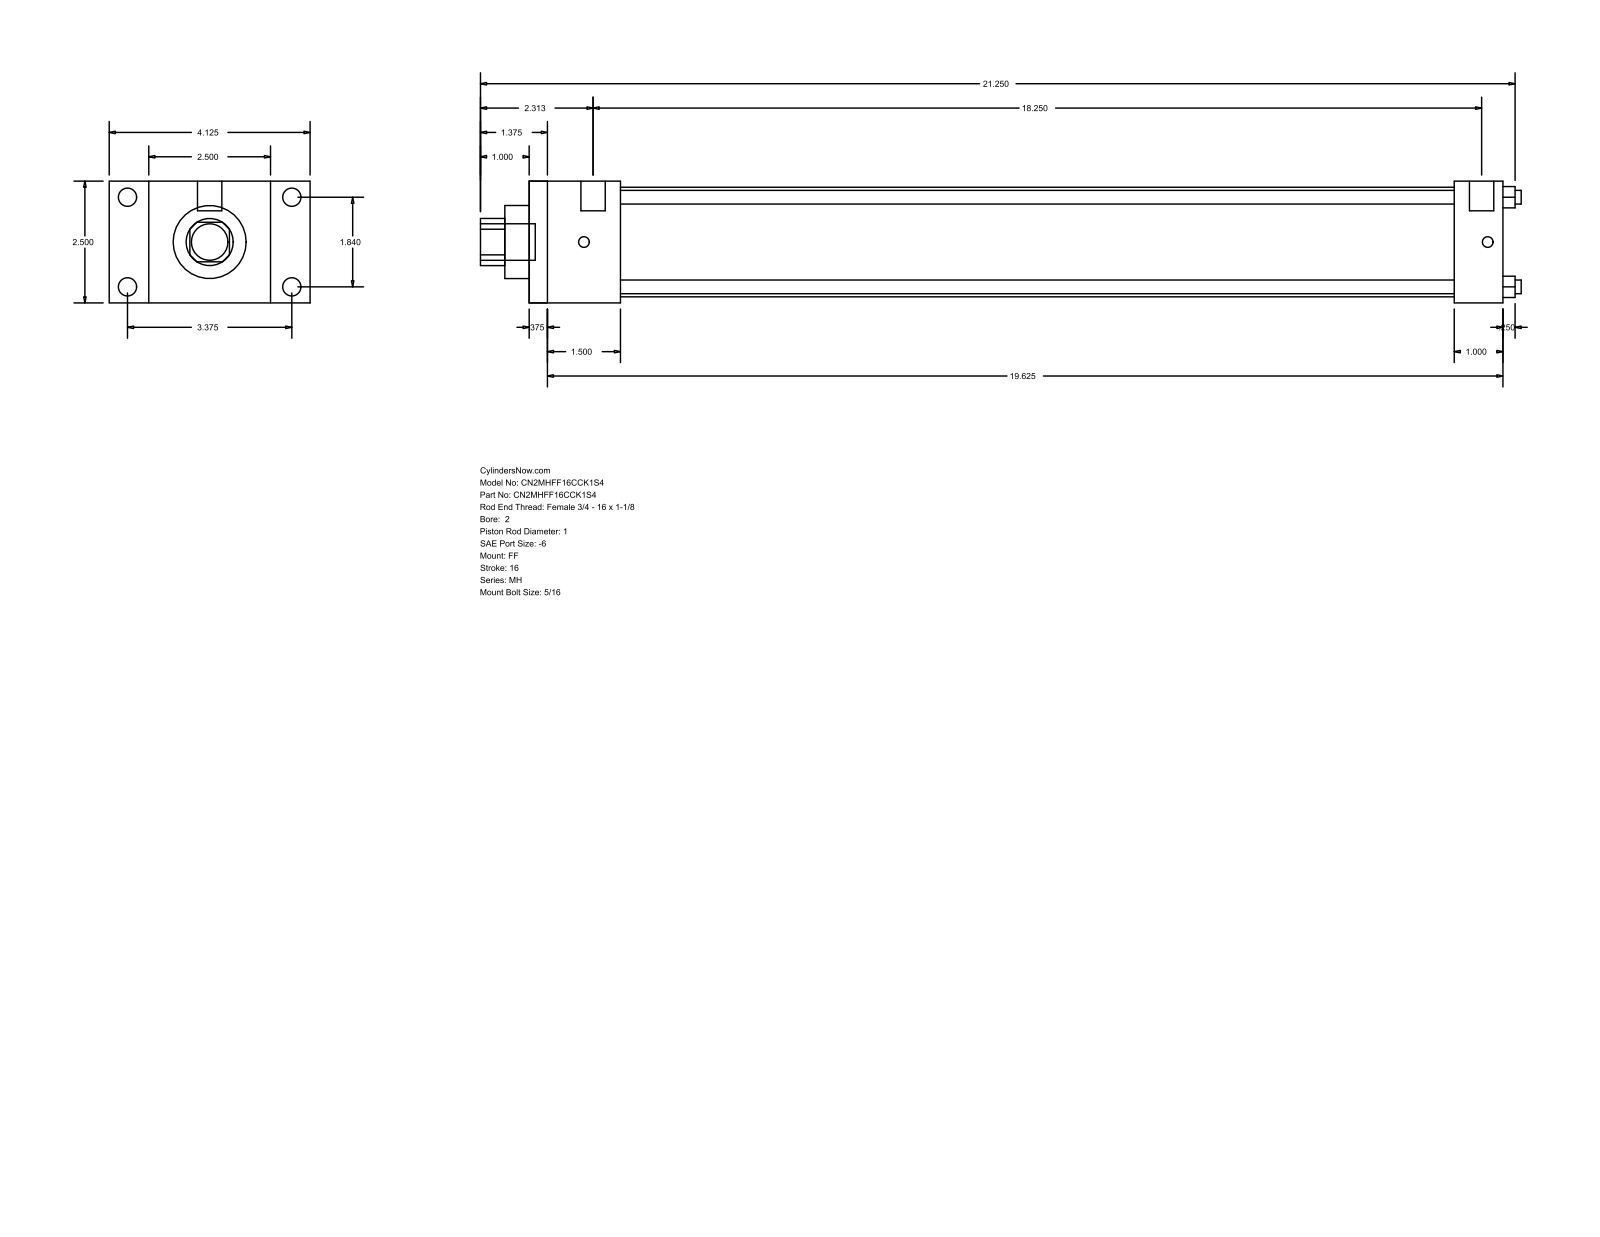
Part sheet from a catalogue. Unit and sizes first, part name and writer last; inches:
Units: inches
Overall size (bounding box): 21.375 × 4.125 × 2.5
Round holes (diameter × count): ⌀0.281 ×4, ⌀1 ×1, ⌀1.5 ×1, ⌀2.25 ×1
Round bosses / shafts (diameter × count): ⌀0.375 ×4, ⌀0.219 ×4, ⌀0.5 ×2, ⌀0.75 ×1
Partial cylindrical surfaces — rounded edges, fillets, slot ends (radius × count): R0.484 ×1
Main face-to-face distances: 2.5, 20, 0.375, 19.625, 0.813, 1, 1.875, 19, 1.5, 18.625
Hole centre spacings: 1.301, 1.84, 2.602
Bodies: 0 solids, 92 faces (64 planar, 28 cylindrical, 0 other)
Part name (STEP PRODUCT): MH_FF__0200_1
STEP written by: GSSL Pune (CONFIG_CONTROL_DESIGN)
